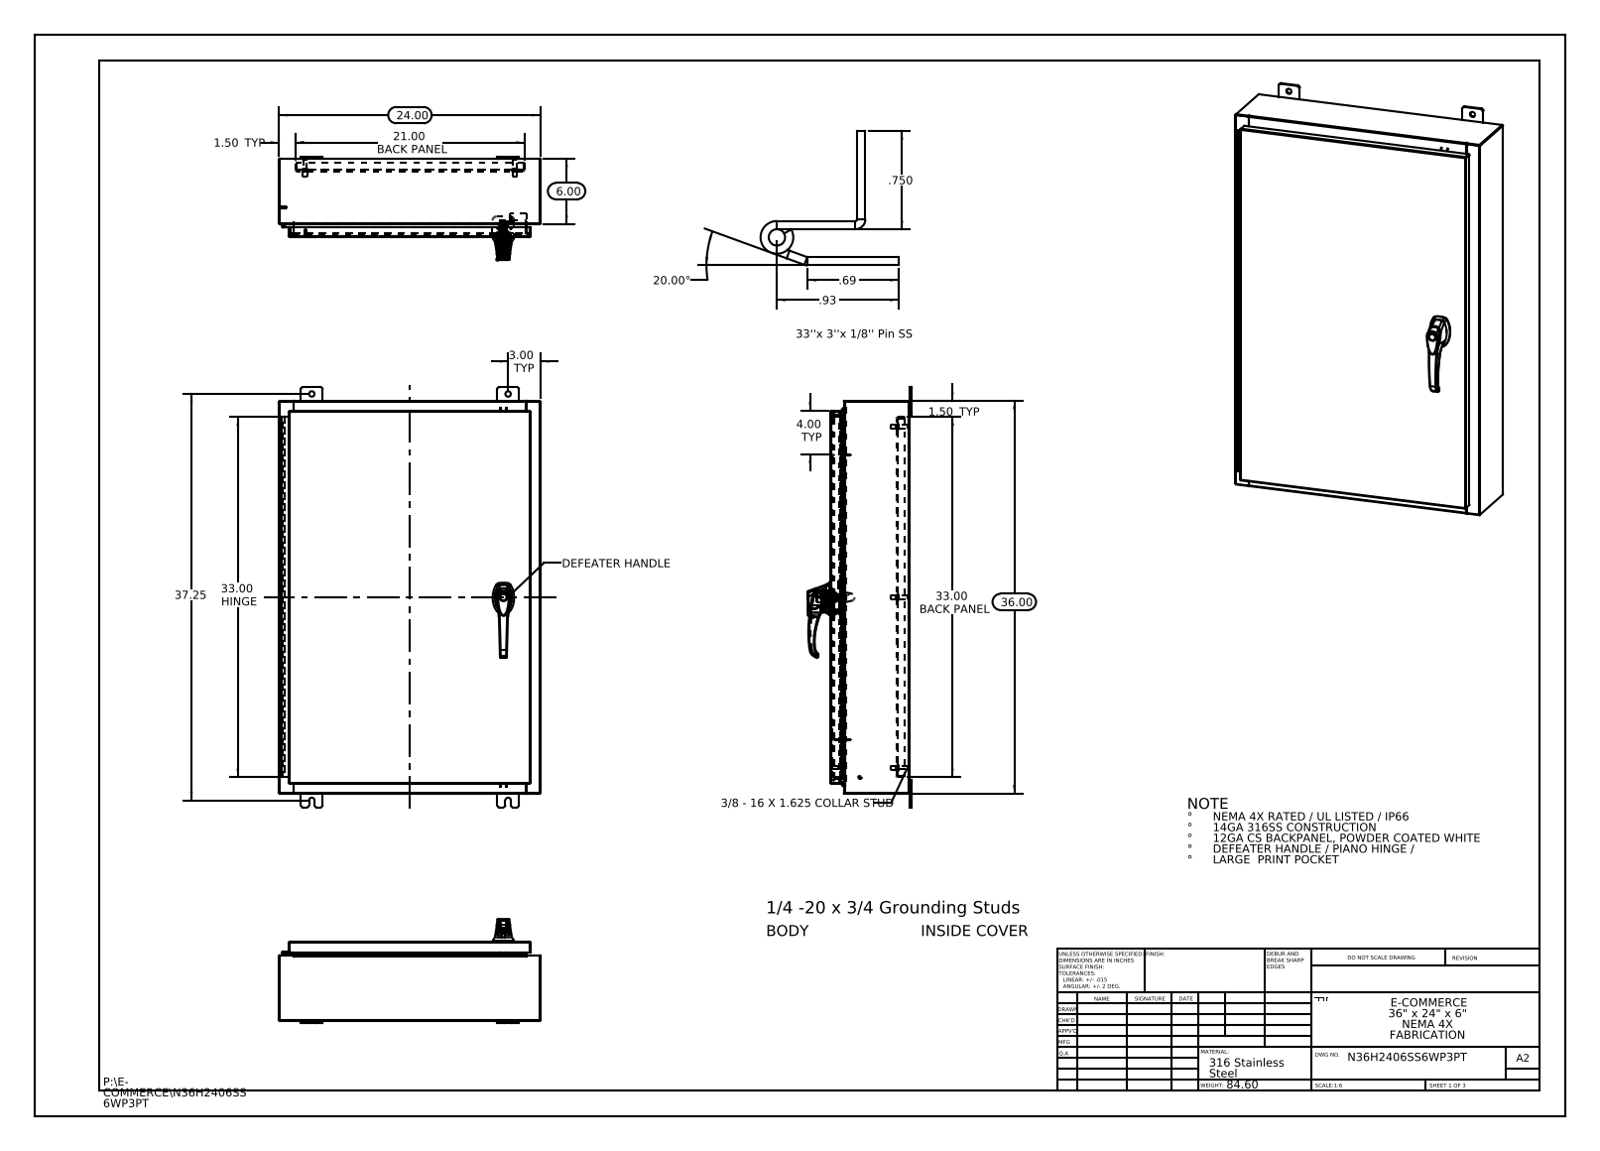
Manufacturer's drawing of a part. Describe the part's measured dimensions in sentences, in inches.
The part is named "N36H2406SS6WP3PT; 297026; 022151; N36H2406SS6WP3PT 125 Pin Hinge (+8 more)". Its 3-D file was written by "SolidWorks 2013 (CONFIG_CONTROL_DESIGN)". It is 39 solids with 2856 faces: 1053 planar, 1085 cylindrical and 718 other. Overall it measures 38.5 by 24 by 9.495 inches. Its volume is 300.7 cubic inches and its surface area 7 381 square inches. Round holes: 10 of diameter 0.5, 4 of diameter 0.25, 3 of diameter 0.138, 3 of diameter 0.161, 2 of diameter 0.079, 2 of diameter 0.203, 2 of diameter 0.313, 2 of diameter 0.437, 1 of diameter 0.125, 1 of diameter 0.125, 1 of diameter 0.197, 1 of diameter 0.276. Round bosses or shafts: 6 of diameter 0.625, 6 of diameter 0.375, 6 of diameter 0.33, 4 of diameter 0.157, 4 of diameter 0.14, 3 of diameter 0.315, 3 of diameter 0.236, 1 of diameter 1.181. Partial cylindrical surfaces (rounded edges, fillets, slot ends): 37 of radius 0.118, 33 of radius 0.006, 24 of radius 0.013, 24 of radius 0.19, 18 of radius 0.088, 15 of radius 0.039, 12 of radius 0.028, 6 of radius 0.008. The main face-to-face distances are 0.075, 7.126, 0.104, 7.051, 7.201, 1, 1.075, 6.051, 6.126, 1.179. The hole center spacings are 11.363, 13.669, 15.625, 24.793, 19.25, 0.295, 0.625, 0.841.
